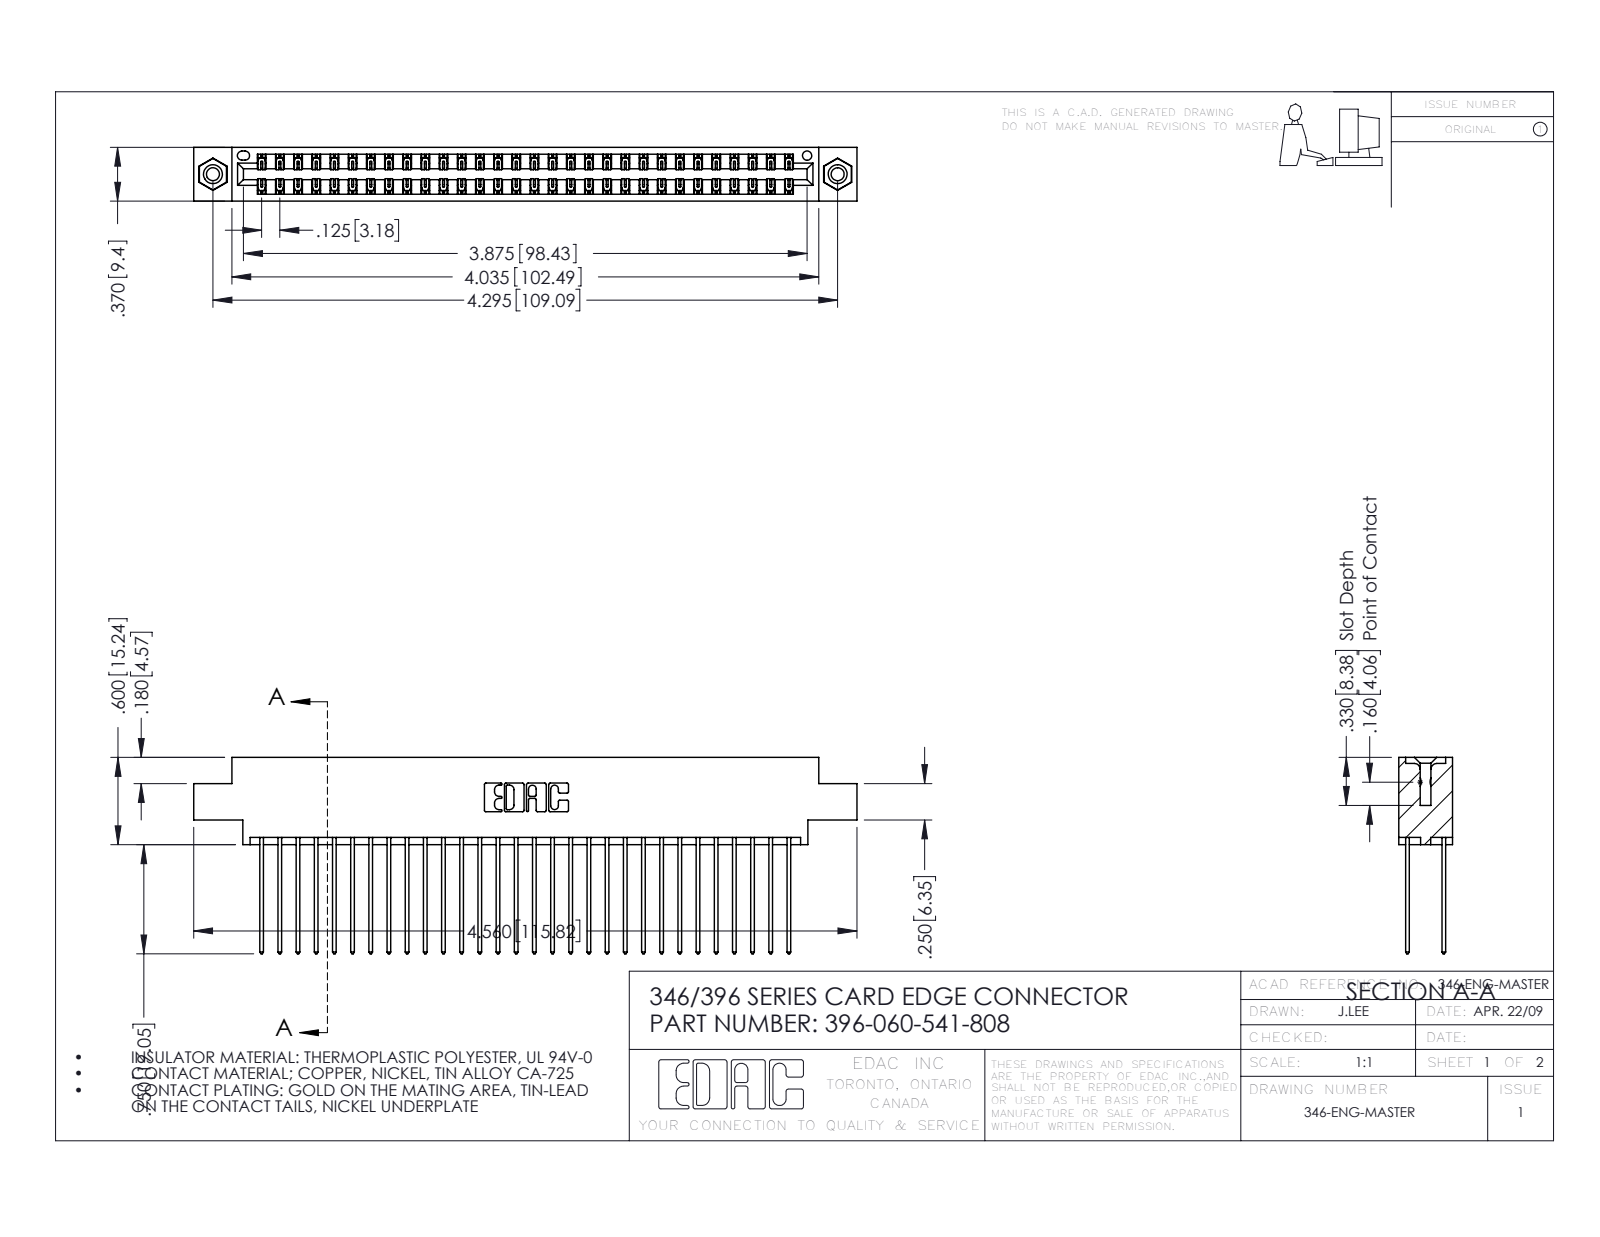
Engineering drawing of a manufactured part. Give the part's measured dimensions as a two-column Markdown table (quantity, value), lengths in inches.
| quantity | value |
| --- | --- |
| part name | 346 Part_0.170 Offset - 0.156 Dia-TI; 396-060-541-808; 345-250-001_345-250-003-102; 345-292-001_345-293-141 |
| STEP written by | SolidWorks 2016 (CONFIG_CONTROL_DESIGN) |
| units | inches |
| bodies | 63 solids, 3306 faces (2212 planar, 1078 cylindrical, 16 other) |
| overall size | 4.56 × 1.35 × 0.37 |
| volume | 0.695 in³ |
| surface area | 26.83 in² |
| round holes (diameter × count) | 0.089 × 2, 0.125 × 2, 0.156 × 2, 0.064 × 1 |
| round bosses / shafts (diameter × count) | 0.155 × 2 |
| partial cylindrical surfaces (radius × count) | 0.006 × 90, 0.01 × 60, 0.01 × 22, 0.007 × 6, 0.031 × 6, 0.026 × 3, 0.014 × 2, 0.022 × 2 |
| main face-to-face distances | 0.048, 0.322, 0.25, 0.072, 0.298, 0.025, 0.37, 0.275, 0.222, 0.148 |
| hole center spacings | 0.246, 4.087, 4.295 |
